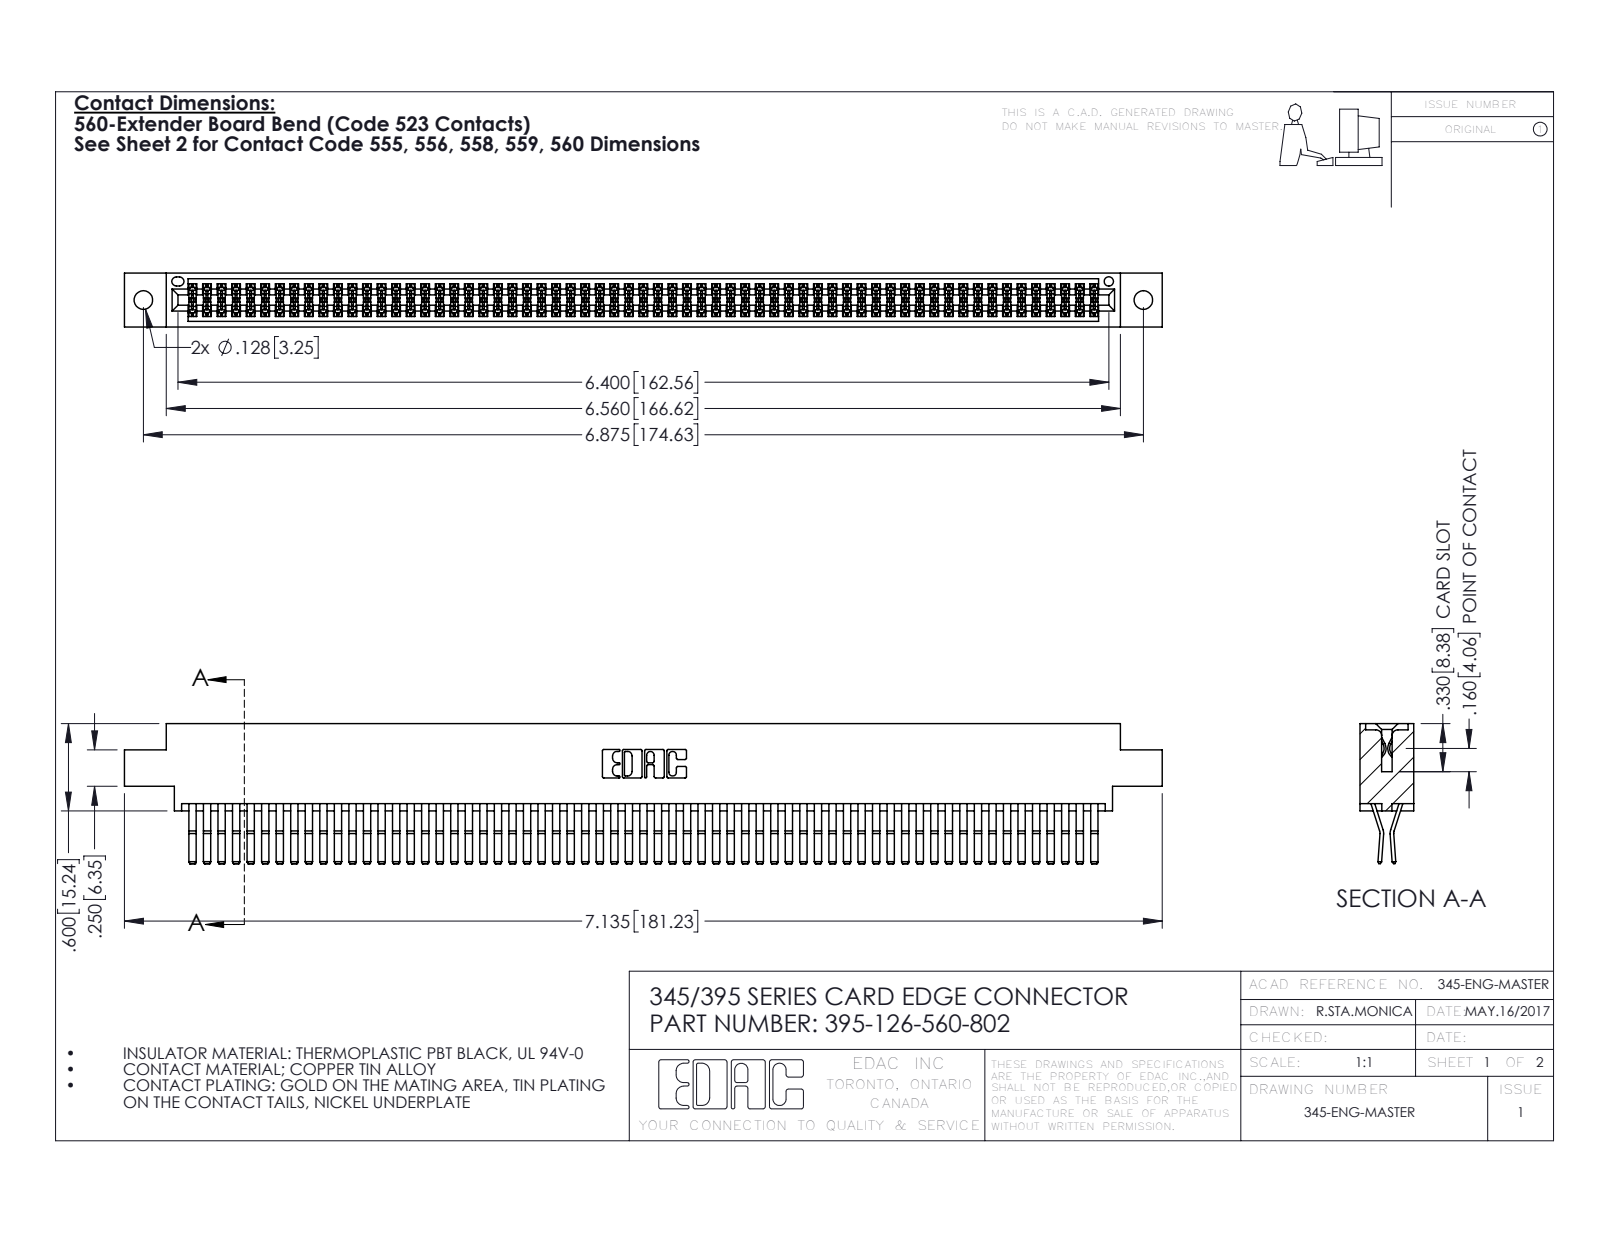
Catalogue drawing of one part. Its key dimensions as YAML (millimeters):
part_name: "345-292-001_560 Tail; 345 Part_0.170 Offset - 0.128 Dia; 395-126-560-802"
step_written_by: "SolidWorks 2016 (CONFIG_CONTROL_DESIGN)"
units: millimeters
bodies: {solids: 127, faces: 6682, planar: 4242, cylindrical: 2440, other: 0}
overall_size: [181.2, 24.4, 9.4]
volume: 18470
surface_area: 29710
round_holes:
  - {diameter: 3.3, count: 2}
  - {diameter: 1.6, count: 1}
partial_cylinders:
  - {radius: 0.2, count: 190}
  - {radius: 0.3, count: 22}
  - {radius: 0.2, count: 6}
  - {radius: 0.8, count: 6}
  - {radius: 0.7, count: 3}
  - {radius: 0.3, count: 2}
  - {radius: 0.4, count: 2}
  - {radius: 0.5, count: 2}
face_to_face_distances: [0.6, 7.6, 1.8, 9.4, 5.1, 2.5, 6.9, 5.7, 4.4, 3.8]
hole_center_spacings: [6.9, 168.6, 174.6]
